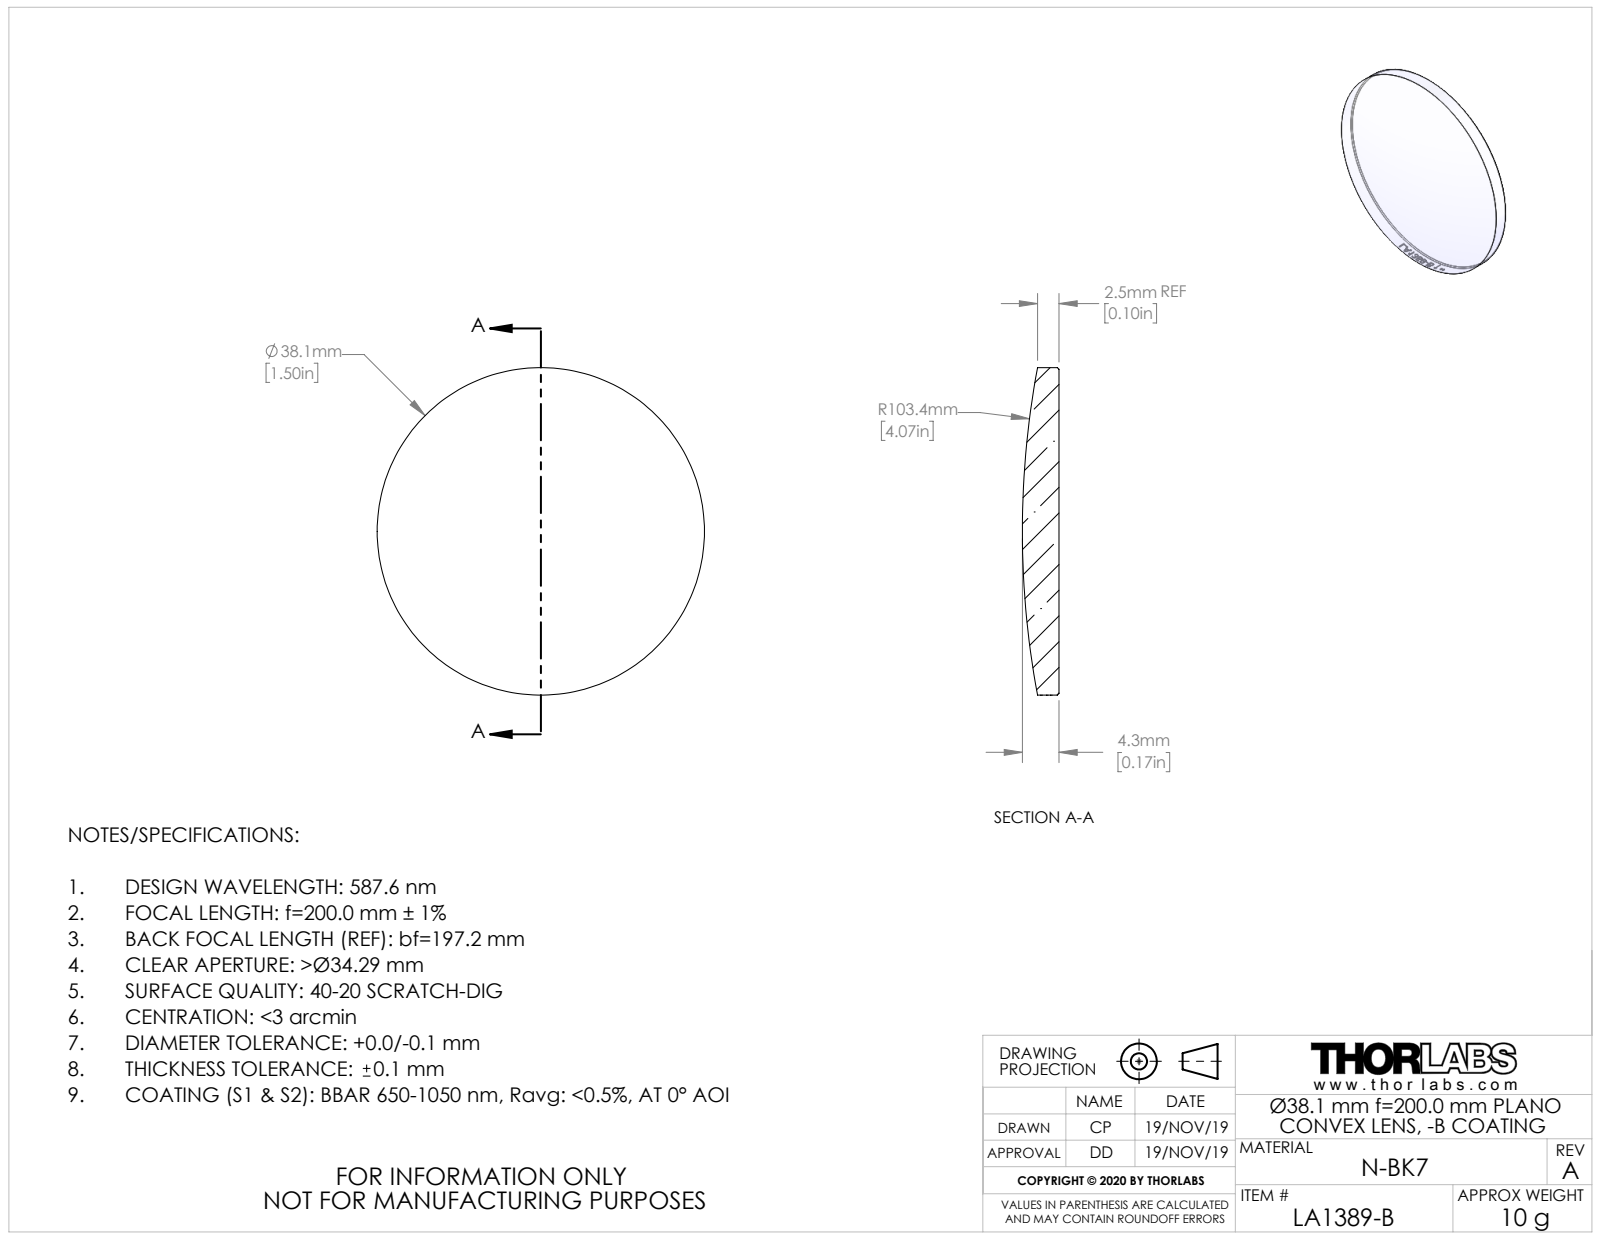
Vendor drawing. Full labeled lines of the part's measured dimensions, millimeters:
Part name (STEP PRODUCT): TTN200730-E0W
STEP written by: SolidWorks 2018 (CONFIG_CONTROL_DESIGN)
Units: millimetres
Bodies: 1 solid, 25 faces (1 planar, 20 cylindrical, 4 other)
Overall size (bounding box): 38.1 × 38.1 × 4.27
Volume: 3 859 mm³ · Surface area: 2 575 mm²
Round bosses / shafts (diameter × count): ⌀38.1 ×1
